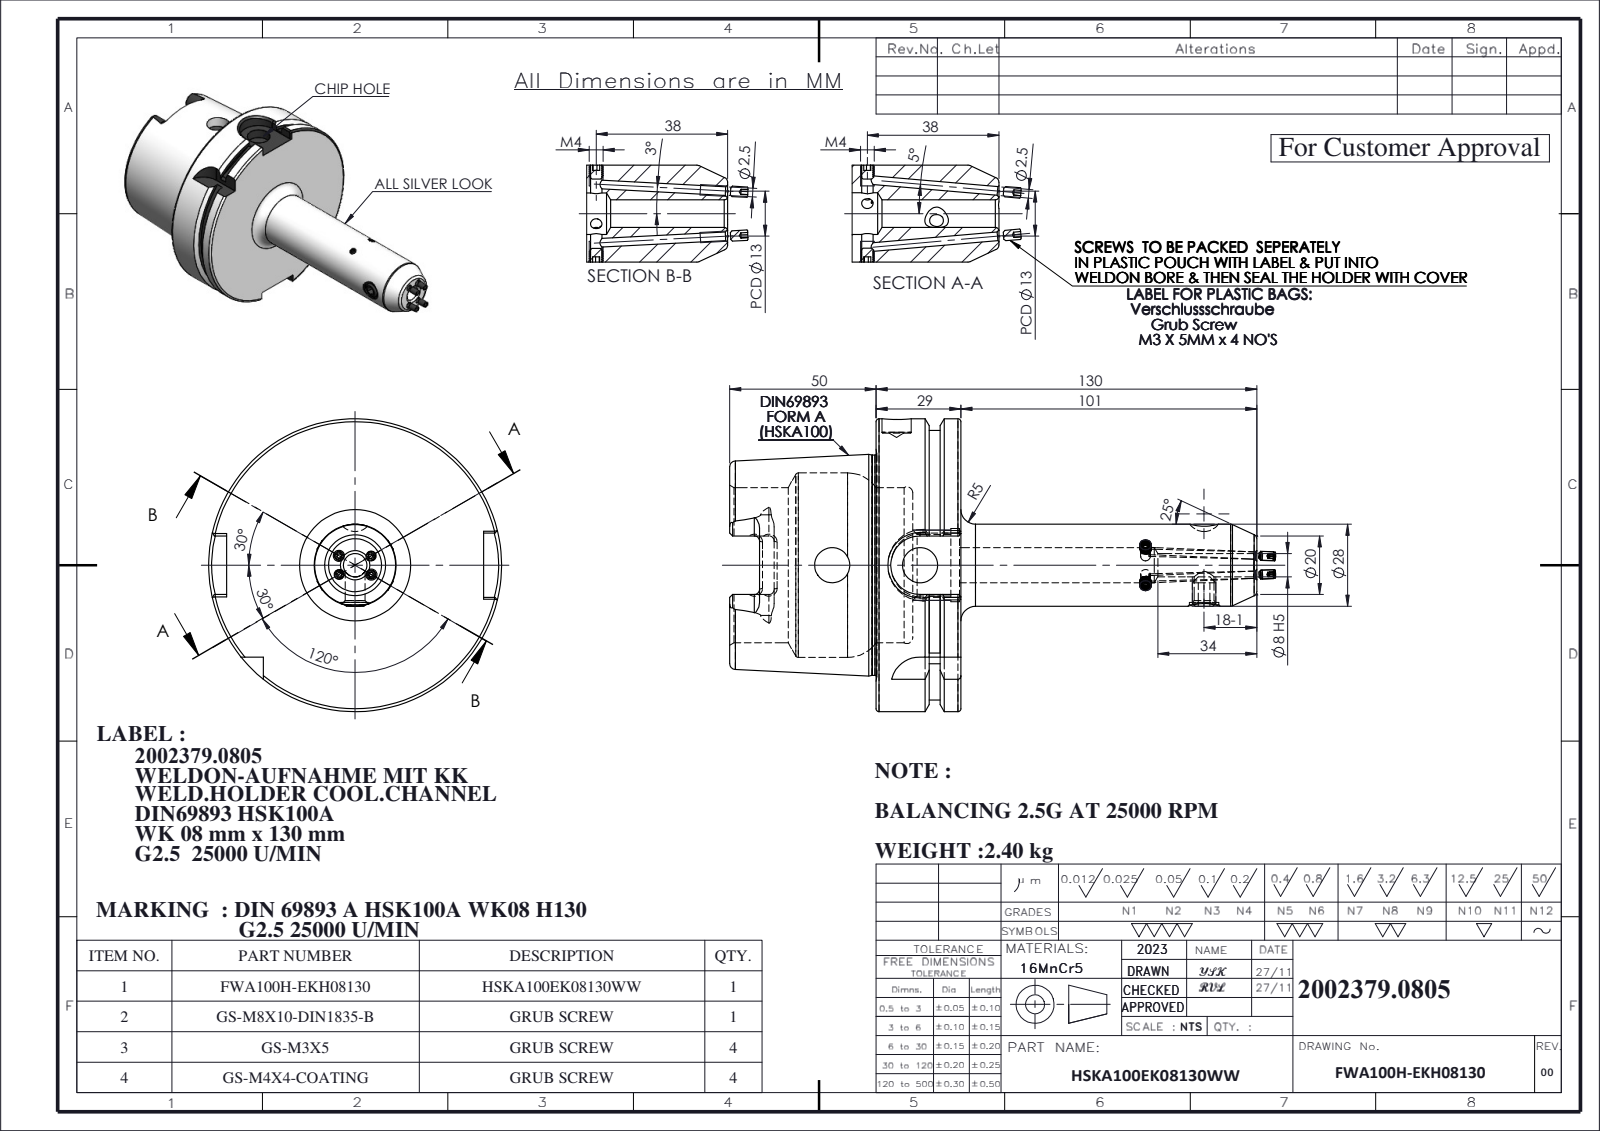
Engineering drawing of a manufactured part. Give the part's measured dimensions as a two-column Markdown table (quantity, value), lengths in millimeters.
| quantity | value |
| --- | --- |
| part name | GS-M3X5; GS-M8X10-DIN1835-B; FWA100H-EKH08130; GS-M4X4_DIN 913 - M4 x 4-N (+1 more) |
| STEP written by | SolidWorks 2023 (CONFIG_CONTROL_DESIGN) |
| units | millimeters |
| bodies | 10 solids, 501 faces (153 planar, 120 cylindrical, 228 other) |
| overall size | 186.44 × 100 × 100 |
| volume | 304 784 mm³ |
| surface area | 64 100 mm² |
| round holes (diameter × count) | 2.5 × 4, 3.3 × 3, 12 × 3, 10 × 2, 6.8 × 1, 8 × 1, 21 × 1, 25 × 1, 53 × 1, 63 × 1 |
| round bosses / shafts (diameter × count) | 3 × 4, 4 × 3, 100 × 1, 92 × 1, 75.16 × 1, 28 × 1, 8 × 1 |
| partial cylindrical surfaces (radius × count) | 1.8 × 6, 4.88 × 4, 10 × 2, 11 × 1 |
| main face-to-face distances | 28.95, 12.5, 16.45, 50, 62.5, 78.95, 16, 71.88, 21.88, 9.38 |
| hole center spacings | 30, 105 |
